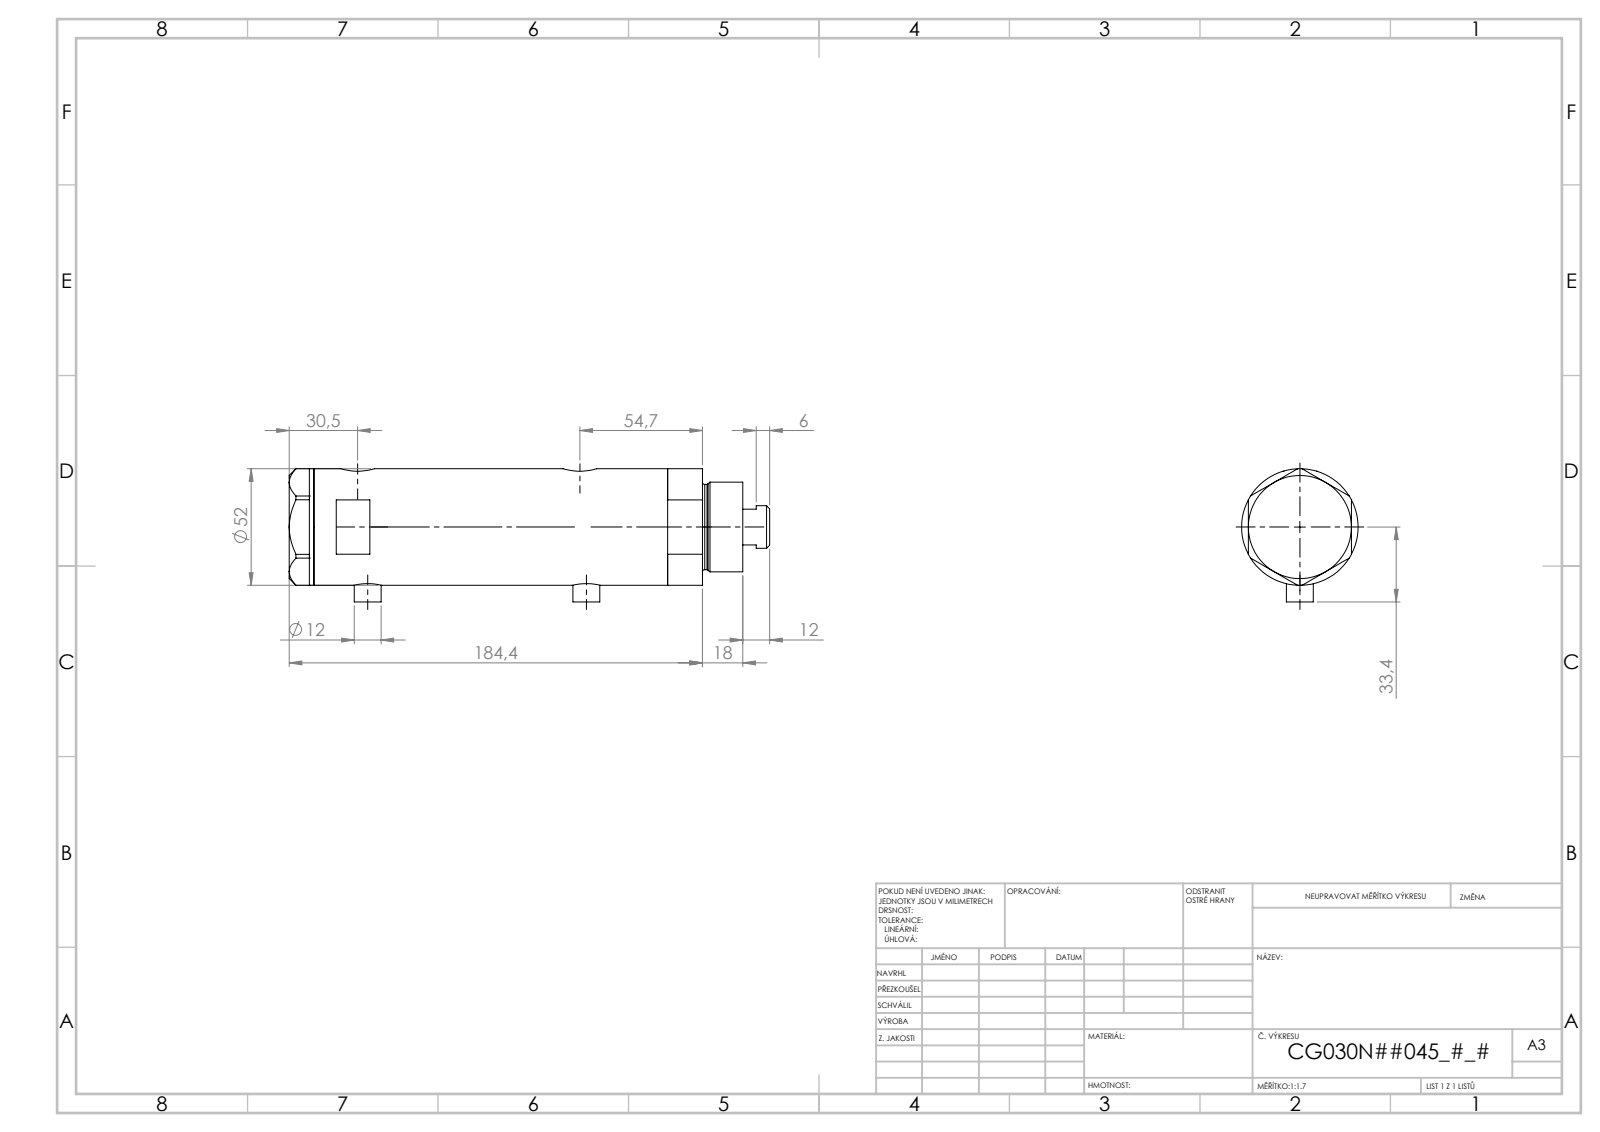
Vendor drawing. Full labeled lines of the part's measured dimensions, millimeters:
Part name (STEP PRODUCT): V270CG_BACK; V270CG_VC; V270CG_MIDDLE; V270CG_FRONT
STEP written by: SolidWorks 2019 (CONFIG_CONTROL_DESIGN)
Units: millimetres
Bodies: 4 solids, 140 faces (67 planar, 53 cylindrical, 20 other)
Overall size (bounding box): 194.02 × 53.1 × 52
Volume: 345 414 mm³ · Surface area: 79 509 mm²
Round holes (diameter × count): ⌀5 ×2, ⌀9.73 ×2, ⌀12.5 ×2, ⌀15 ×2, ⌀6.5 ×1, ⌀20 ×1, ⌀21.5 ×1, ⌀30 ×1, ⌀33 ×1, ⌀44 ×1
Round bosses / shafts (diameter × count): ⌀12 ×2, ⌀52 ×1, ⌀40 ×1, ⌀38 ×1, ⌀19 ×1
Main face-to-face distances: 98.54, 23.8, 74.74, 11, 34.8, 109.54, 46, 145.94, 134.94, 111.14
Hole centre spacings: 2.9, 4.5, 71.75, 74.65, 76.25, 79.15, 2.89, 2.91
